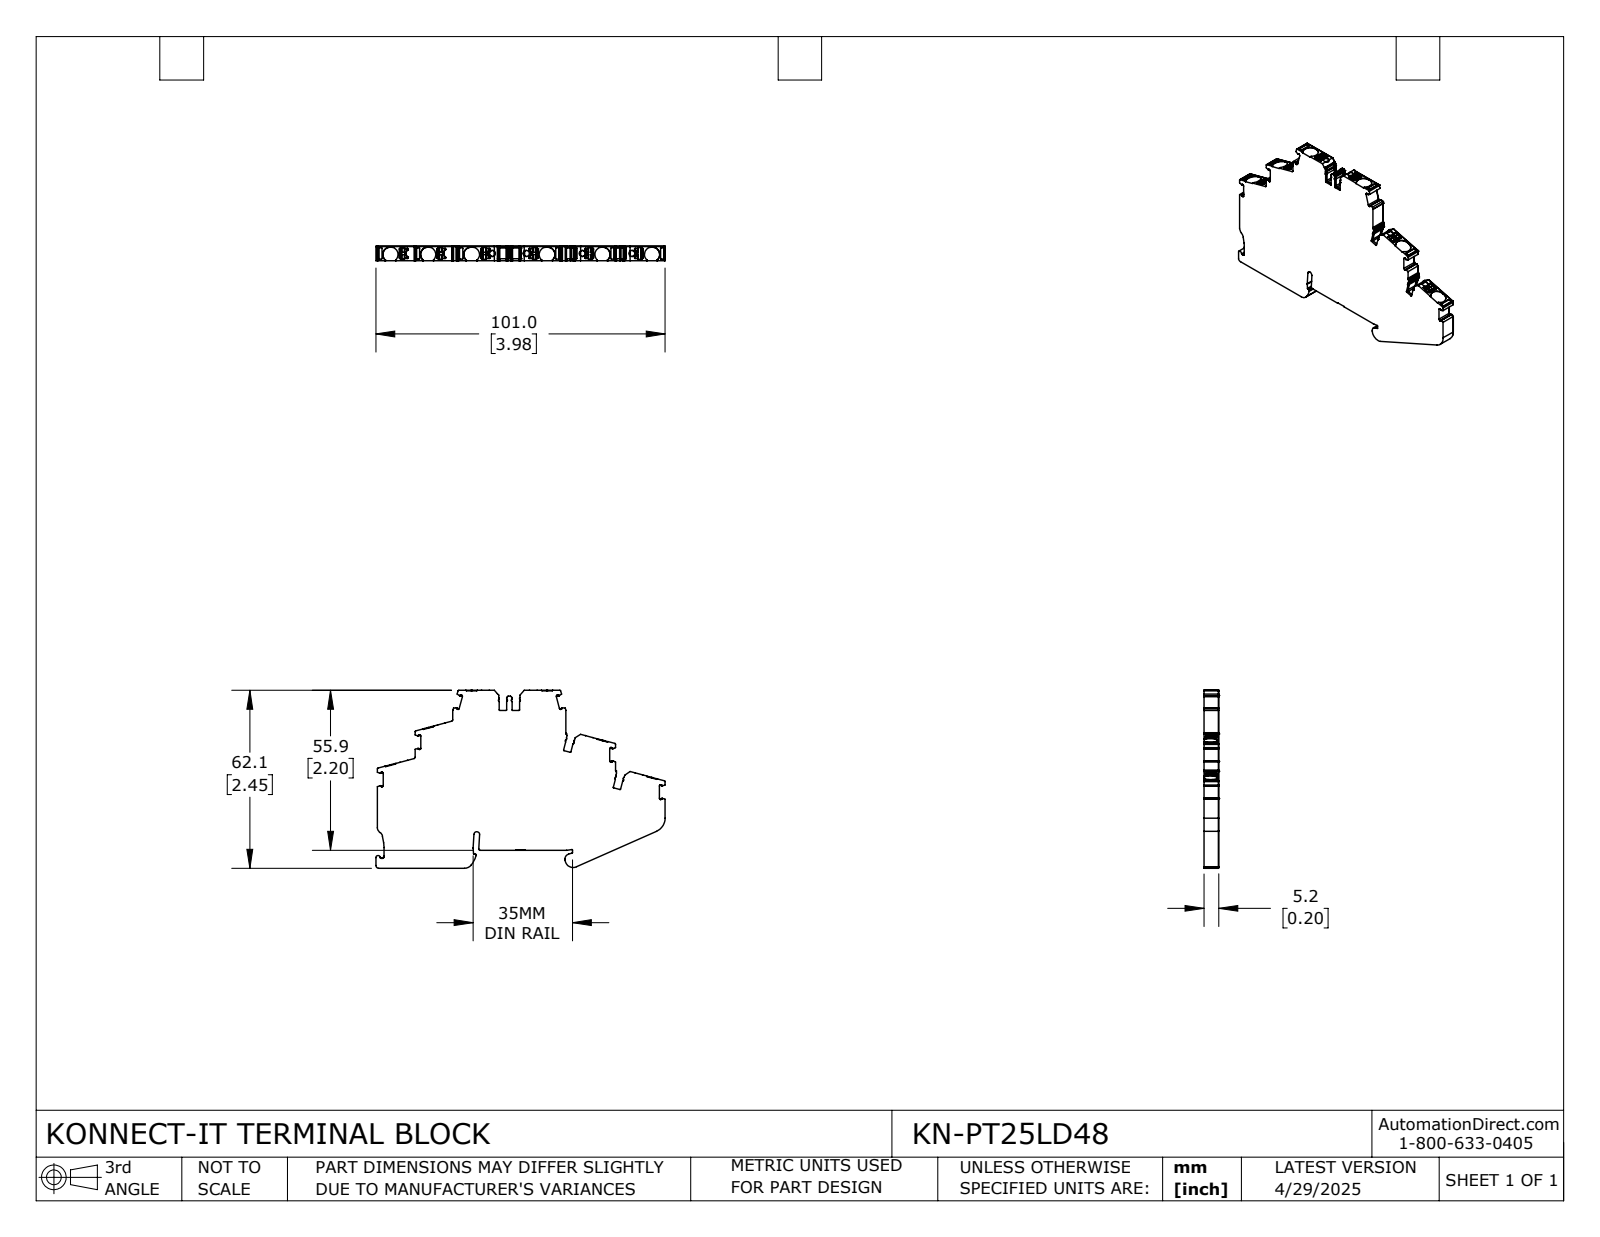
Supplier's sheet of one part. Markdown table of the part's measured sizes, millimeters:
| quantity | value |
| --- | --- |
| part name | KN-PT25LD48 |
| STEP written by | SolidWorks 2024 (CONFIG_CONTROL_DESIGN) |
| units | millimeters |
| bodies | 1 solid, 1212 faces (579 planar, 528 cylindrical, 105 other) |
| overall size | 101 × 62.1 × 5.2 |
| volume | 22 190 mm³ |
| surface area | 10 810 mm² |
| round holes (diameter × count) | 2.1 × 4 |
| partial cylindrical surfaces (radius × count) | 0.2 × 128, 0.1 × 49, 0.3 × 47, 0.5 × 26, 0.2 × 24, 0.4 × 17, 0.6 × 14, 0.2 × 12 |
| main face-to-face distances | 5.2, 6.2, 2, 55.7, 61.9, 8.1, 17.3, 13.2, 62.1, 55.9 |
| hole center spacings | 11.8, 20.1 |
